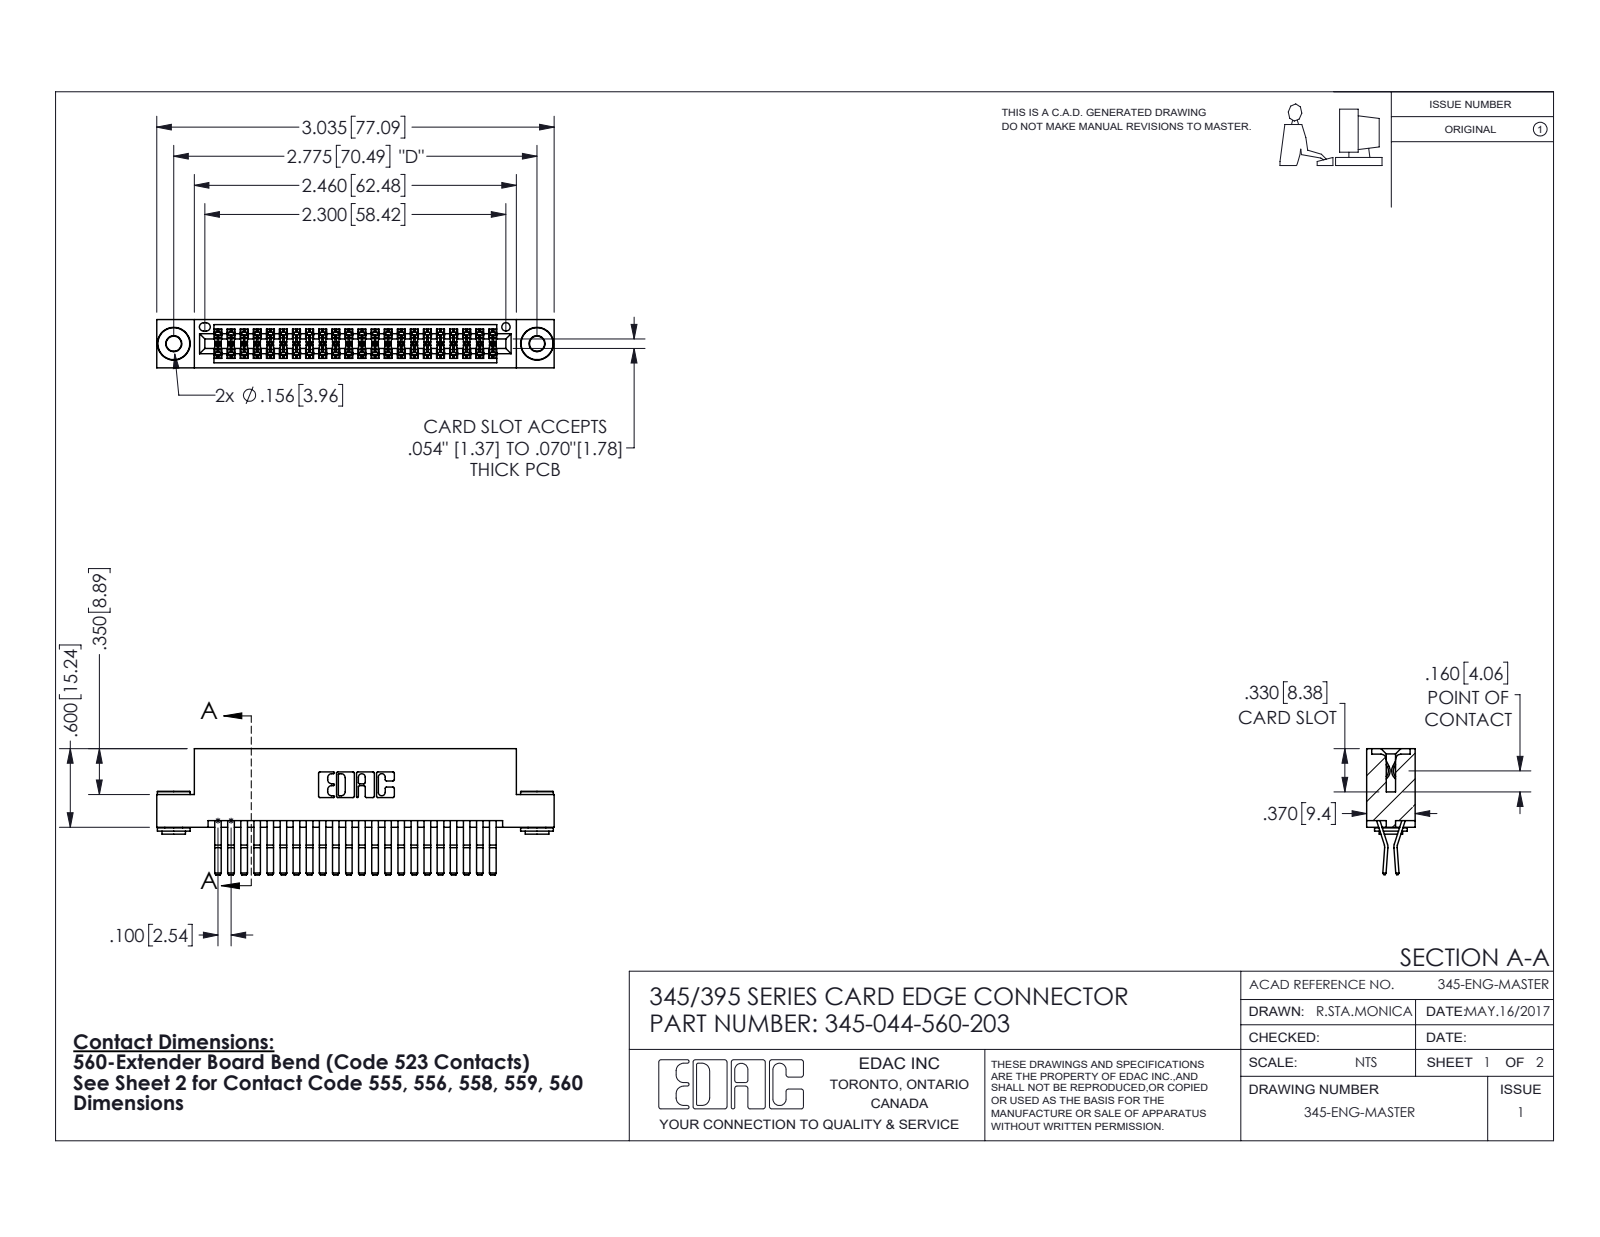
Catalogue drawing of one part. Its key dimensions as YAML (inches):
part_name: "345-044-560-203; 345 Part_Flush Mounting Lugs - 0.156 Dia-TH; 345-292-001_560 Tail; 345-250-002_345-250-002-102"
step_written_by: "SolidWorks 2016 (CONFIG_CONTROL_DESIGN)"
units: inches
bodies: {solids: 47, faces: 2452, planar: 1542, cylindrical: 902, other: 8}
overall_size: [3.035, 0.962, 0.37]
volume: 0.464
surface_area: 18.3
round_holes:
  - {diameter: 0.116, count: 2}
  - {diameter: 0.156, count: 2}
  - {diameter: 0.064, count: 1}
round_bosses_or_shafts:
  - {diameter: 0.25, count: 2}
  - {diameter: 0.18, count: 2}
  - {diameter: 0.136, count: 2}
partial_cylinders:
  - {radius: 0.006, count: 66}
  - {radius: 0.01, count: 22}
  - {radius: 0.007, count: 6}
  - {radius: 0.031, count: 6}
  - {radius: 0.026, count: 3}
  - {radius: 0.01, count: 2}
  - {radius: 0.014, count: 2}
  - {radius: 0.019, count: 2}
face_to_face_distances: [0.025, 0.072, 0.298, 0.2, 0.37, 0.098, 0.272, 0.225, 0.175, 0.149]
hole_center_spacings: [0.27, 2.541, 2.775]
